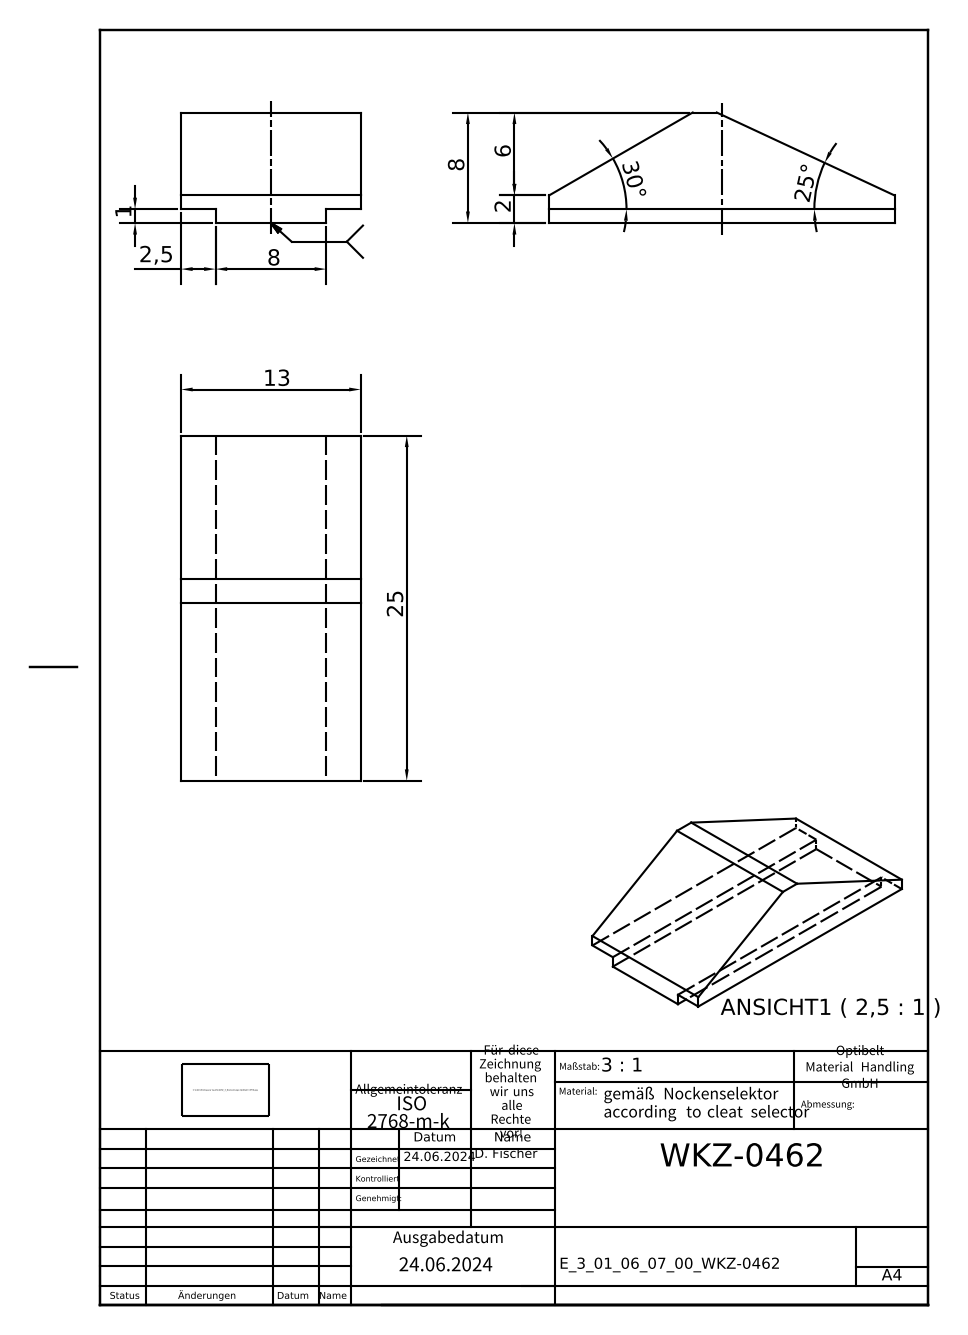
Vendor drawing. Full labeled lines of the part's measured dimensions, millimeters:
Part name (STEP PRODUCT): E_3_01_06_07_00_WKZ-0462
STEP written by: Autodesk Inventor 2025 (AUTOMOTIVE_DESIGN)
Units: millimetres
Bodies: 1 solid, 12 faces (12 planar, 0 cylindrical, 0 other)
Overall size (bounding box): 25 × 13 × 8
Volume: 1 568 mm³ · Surface area: 991 mm²
Main face-to-face distances: 1, 13, 2.5, 10.5, 8, 7, 25
